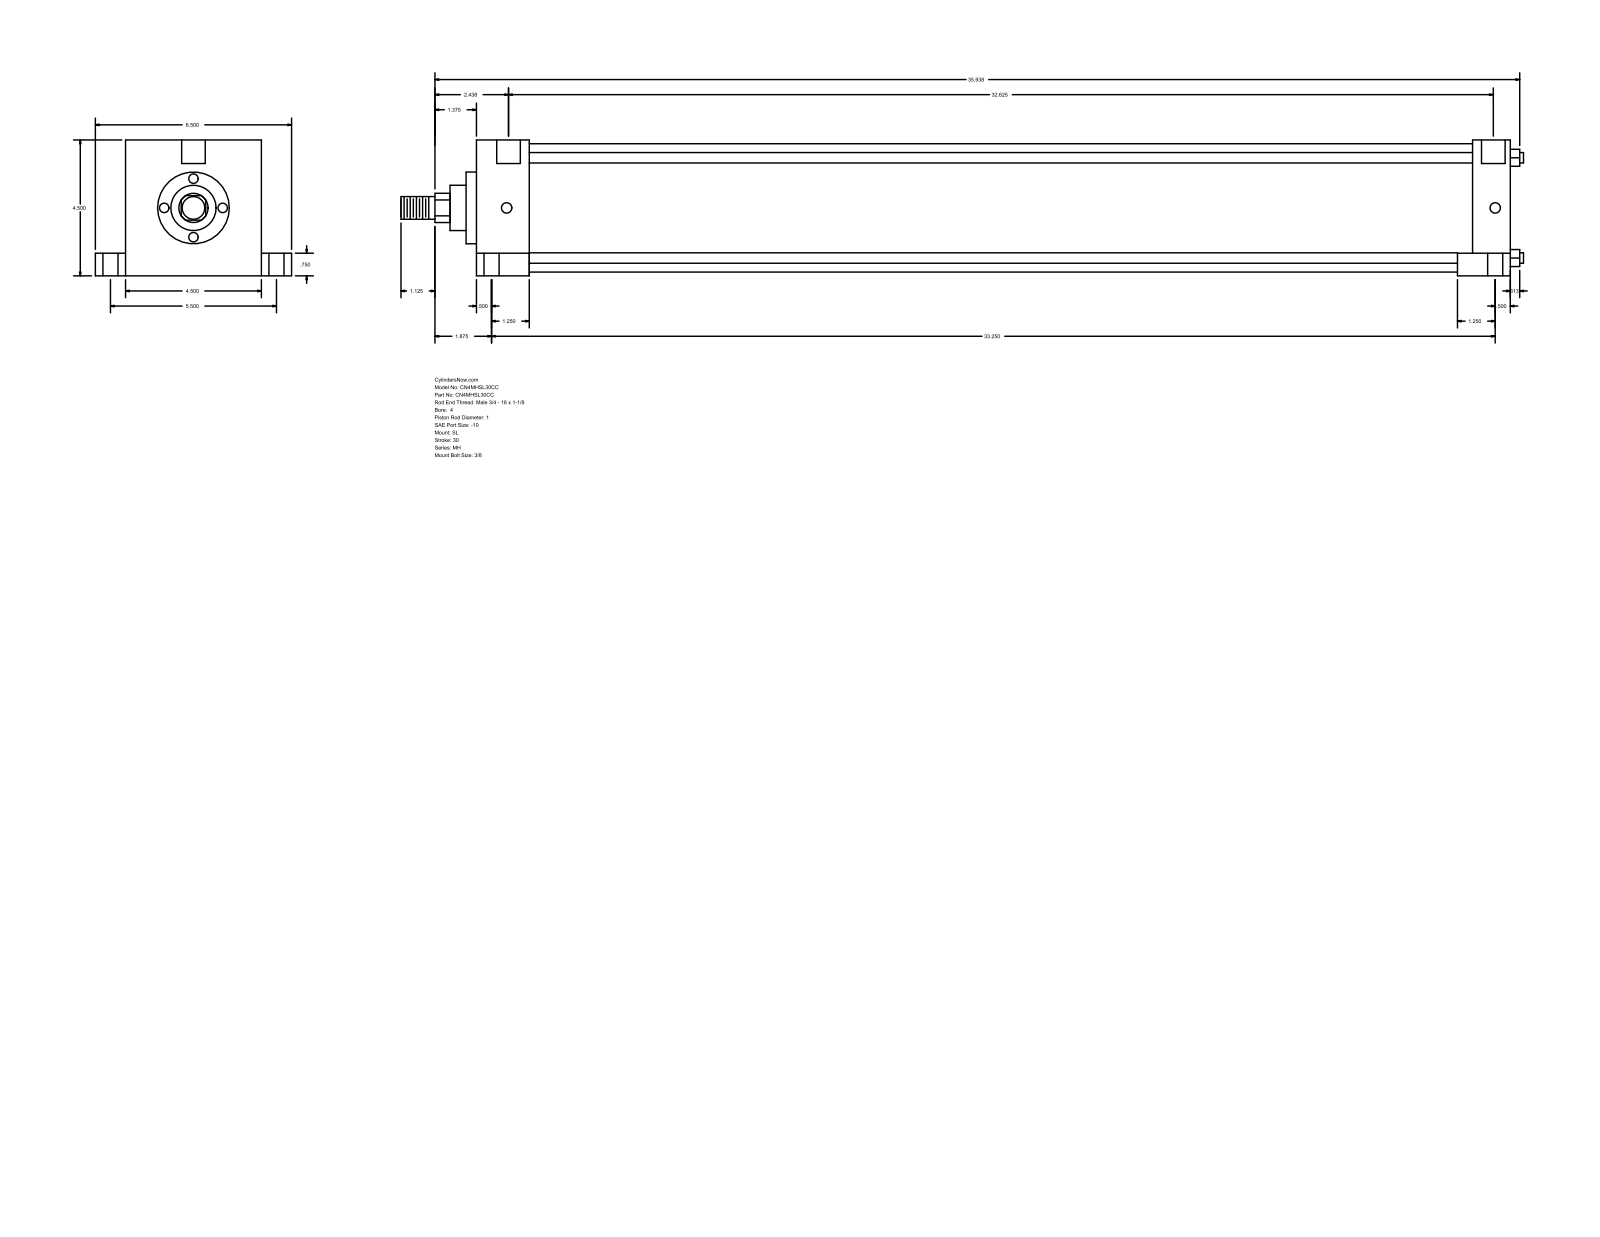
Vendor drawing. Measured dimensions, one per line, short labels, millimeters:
name: MH_SL__0400_1
written by: GSSL Pune (CONFIG_CONTROL_DESIGN)
unit: mm
bodies: 0 solids, 110 faces (77 planar, 33 cylindrical, 0 other)
size: 944.56 × 165.1 × 114.3
holes: 4× ⌀8.73, 4× ⌀12.7, 4× ⌀19.05, 2× ⌀19.84
bosses: 4× ⌀8.76, 1× ⌀107.95, 1× ⌀60.33, 1× ⌀38.1, 1× ⌀25.4, 1× ⌀19.05
rounds: 1× R12.29
face distances: 114.3, 869.96, 44.46, 825.5, 838.2, 793.74, 31.76, 25.4, 139.7, 19.05
hole spacings: 1.58, 69.85, 69.87, 71, 71.3, 139.7, 830.26, 831.84
